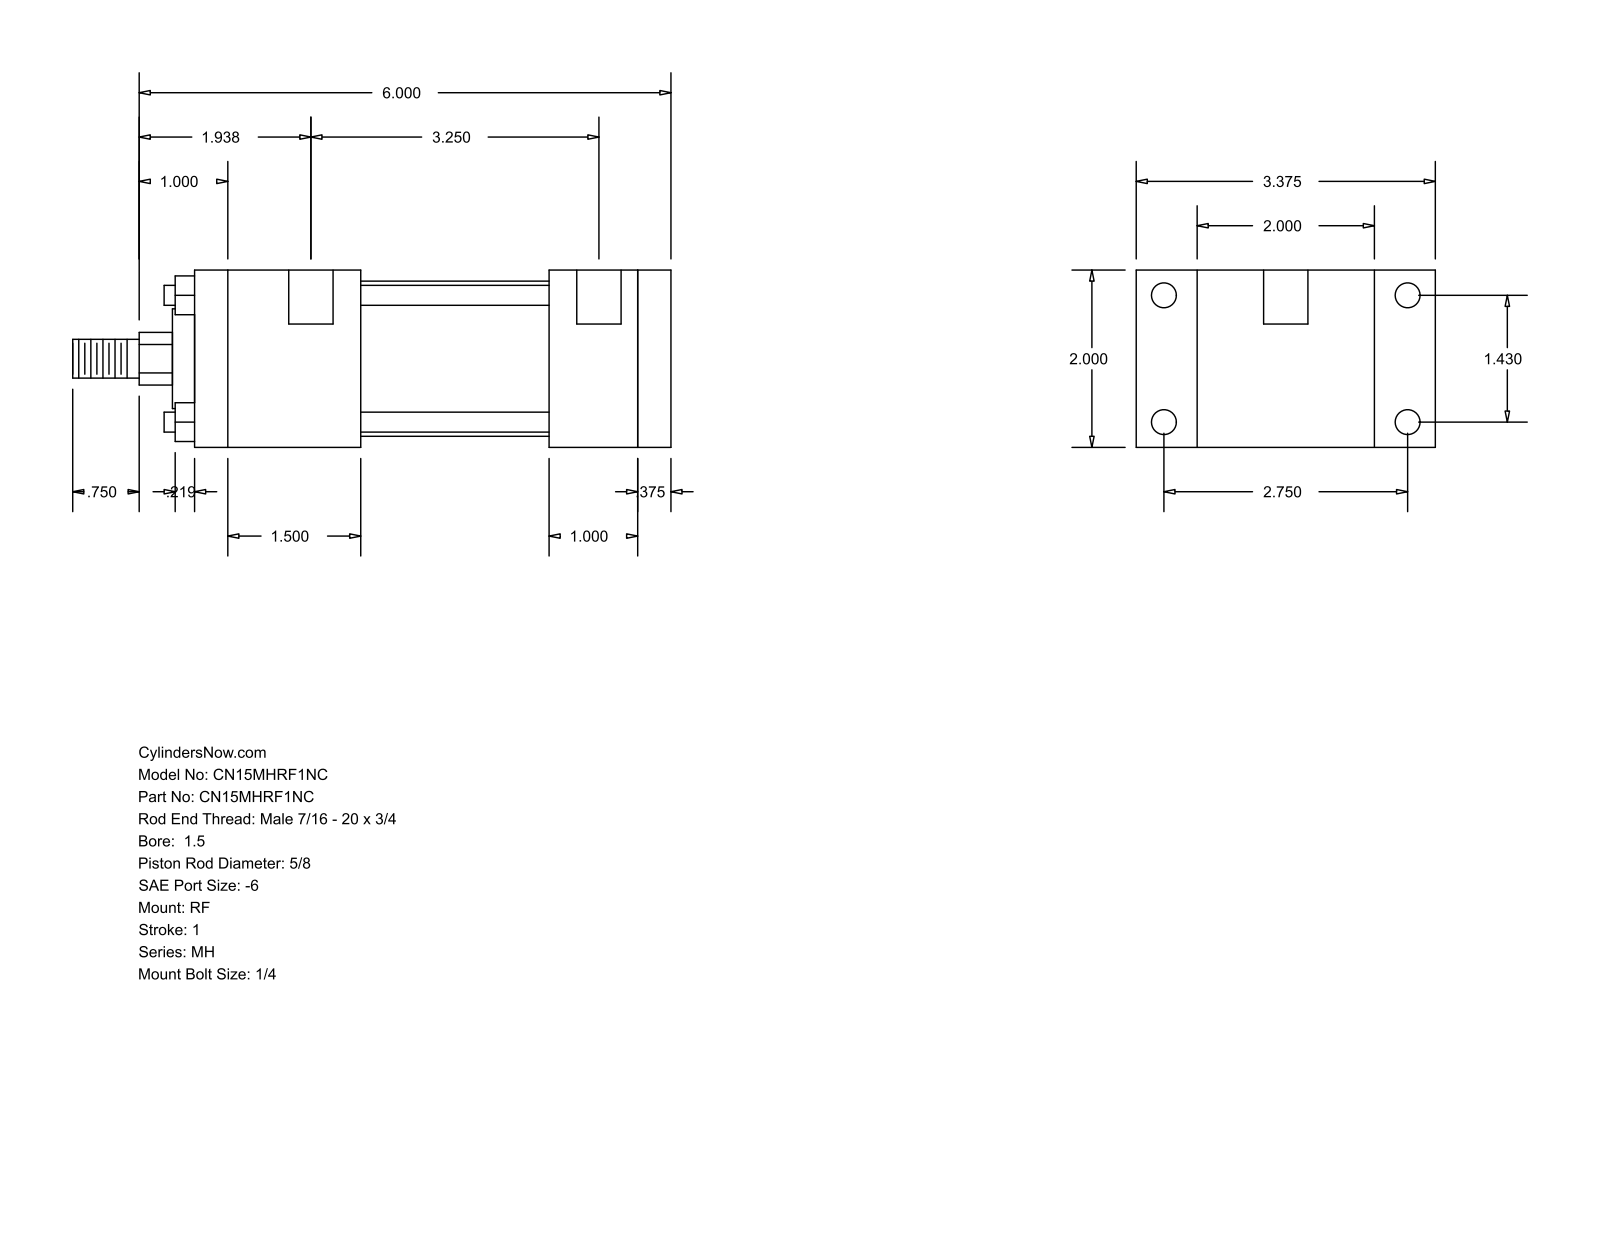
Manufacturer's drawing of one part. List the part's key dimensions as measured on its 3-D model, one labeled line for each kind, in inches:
Part name (STEP PRODUCT): MH_RF__0150_0.625
STEP written by: GSSL Pune (CONFIG_CONTROL_DESIGN)
Units: inches
Bodies: 0 solids, 92 faces (64 planar, 28 cylindrical, 0 other)
Overall size (bounding box): 6.75 × 3.375 × 2
Round holes (diameter × count): ⌀0.219 ×4, ⌀0.281 ×4, ⌀0.5 ×2
Round bosses / shafts (diameter × count): ⌀0.225 ×4, ⌀1.75 ×1, ⌀1.125 ×1, ⌀0.625 ×1, ⌀0.437 ×1
Partial cylindrical surfaces — rounded edges, fillets, slot ends (radius × count): R0.297 ×1
Main face-to-face distances: 2, 0.375, 5.375, 5, 2.125, 1.375, 0.687, 2.687, 4, 1
Hole centre spacings: 1.43, 2.75, 3.099, 3.375, 0.125, 3.25
